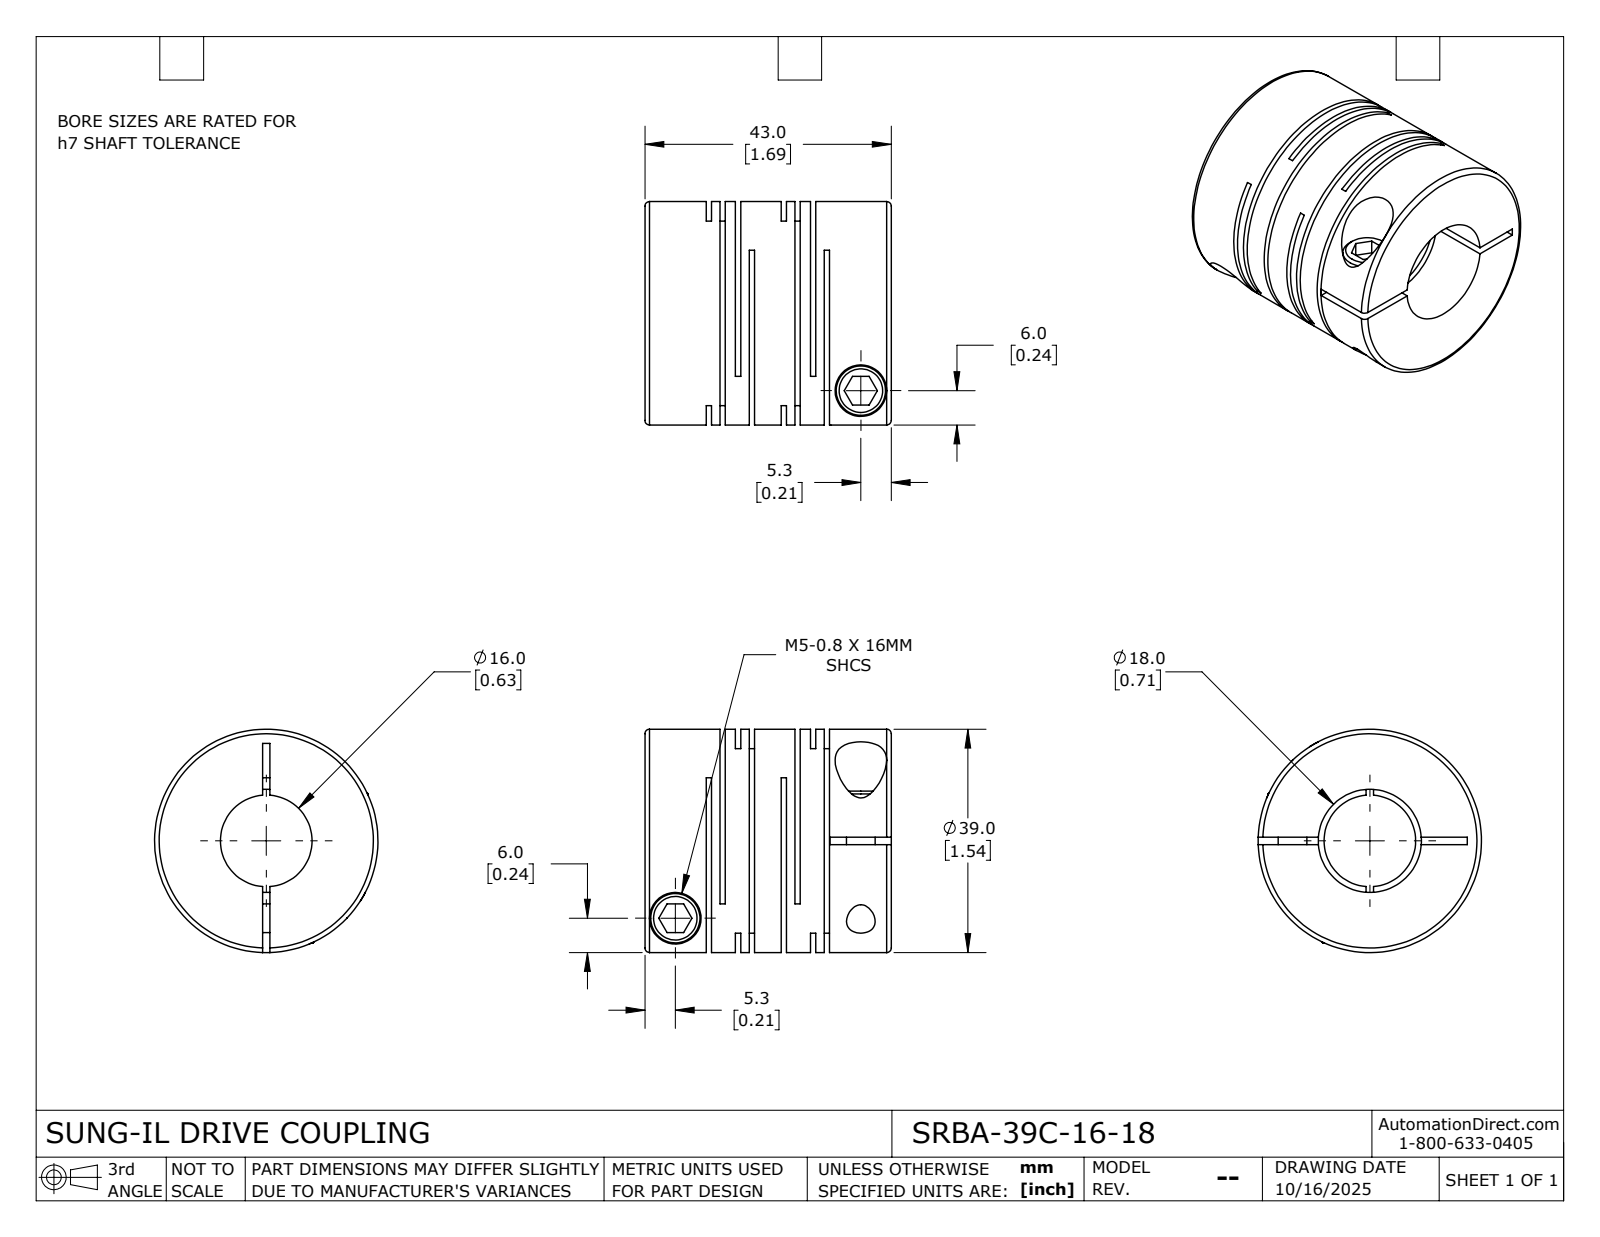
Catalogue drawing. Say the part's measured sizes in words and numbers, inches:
The part is named "SRBA-39C-16-18". Its 3-D file was written by "SolidWorks 2024 (CONFIG_CONTROL_DESIGN)". It is 1 solid with 115 faces: 60 planar, 42 cylindrical and 13 other. Overall it measures 1.693 by 1.535 by 1.535 inches. Its volume is 2.078 cubic inches and its surface area 34.42 square inches. Round holes: 2 of diameter 0.197, 2 of diameter 0.354, 1 of diameter 0.63, 1 of diameter 0.709. Round bosses or shafts: 2 of diameter 0.339, 1 of diameter 1.535. The main face-to-face distances are 0.516, 0.036, 0.094, 0.201, 0.421, 0.552, 0.717, 0.295, 0.48, 0.131.
